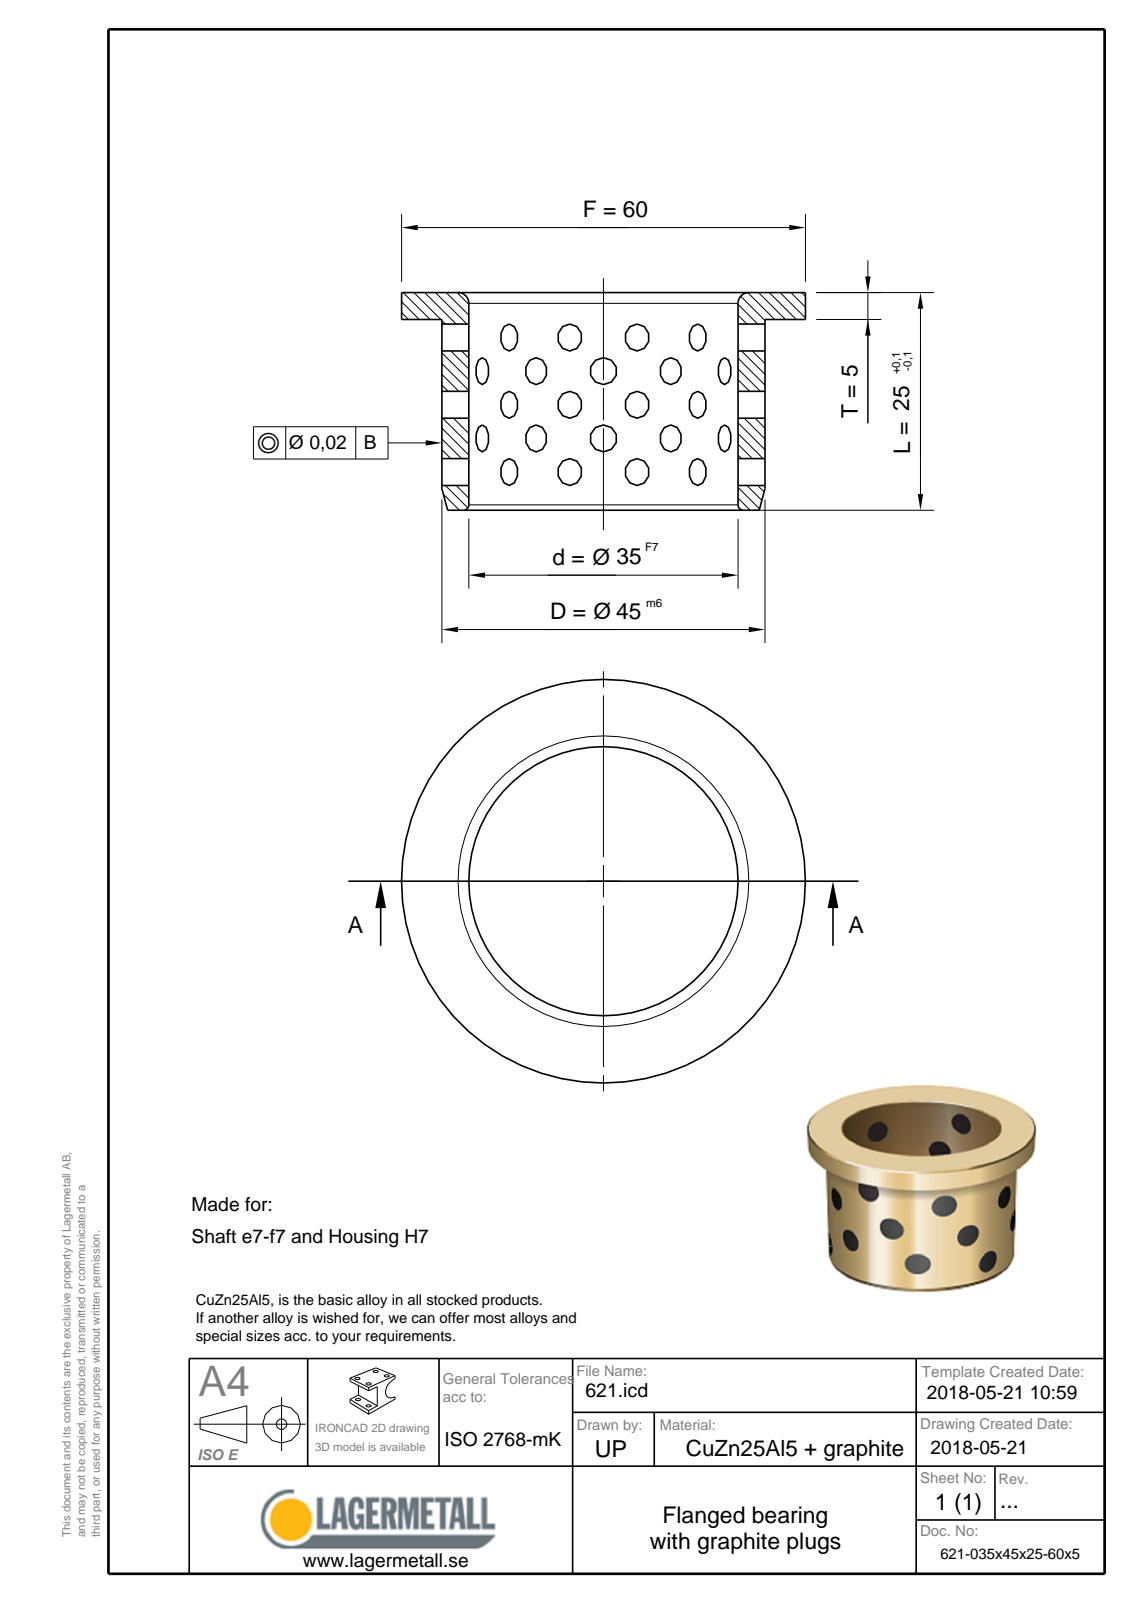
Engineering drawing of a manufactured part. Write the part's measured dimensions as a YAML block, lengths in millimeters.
part_name: "621-035x45x25-60x5"
step_written_by: "Spatial InterOp 3D (CONFIG_CONTROL_DESIGN)"
units: millimeters
bodies: {solids: 1, faces: 9, planar: 3, cylindrical: 3, other: 3}
overall_size: [60, 60, 25]
volume: 21529
surface_area: 9955
round_holes:
  - {diameter: 35, count: 1}
round_bosses_or_shafts:
  - {diameter: 60, count: 1}
  - {diameter: 45, count: 1}
face_to_face_distances: [5, 20, 25]
